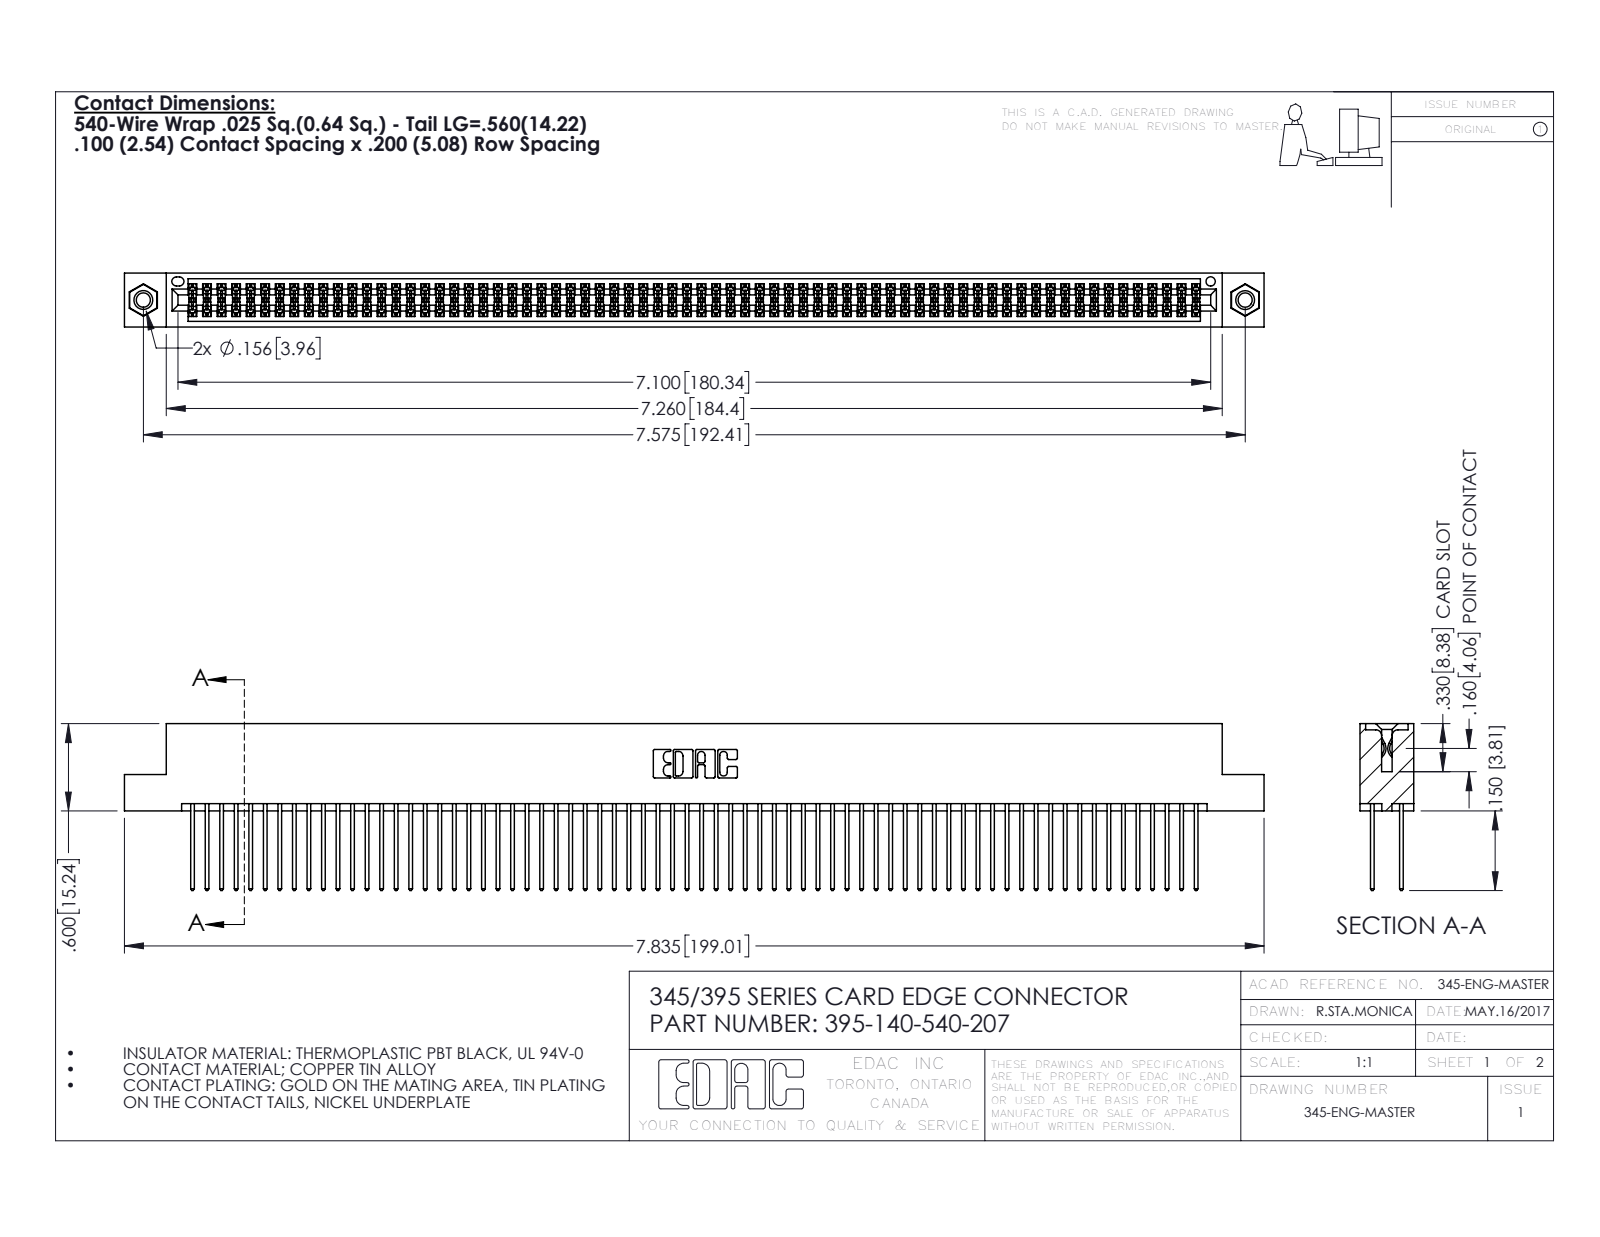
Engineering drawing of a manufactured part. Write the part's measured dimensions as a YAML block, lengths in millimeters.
part_name: "345 Part_Flush Mounting Lugs - 0.156 Dia-TI; 345-250-001_345-250-005-103; 345-292-001_345-293-140; 395-140-540-207"
step_written_by: "SolidWorks 2016 (CONFIG_CONTROL_DESIGN)"
units: millimeters
bodies: {solids: 143, faces: 7186, planar: 4732, cylindrical: 2438, other: 16}
overall_size: [199, 29.1, 9.4]
volume: 20110
surface_area: 32750
round_holes:
  - {diameter: 2.5, count: 2}
  - {diameter: 3.2, count: 2}
  - {diameter: 4, count: 2}
  - {diameter: 1.6, count: 1}
round_bosses_or_shafts:
  - {diameter: 3.9, count: 2}
partial_cylinders:
  - {radius: 0.2, count: 210}
  - {radius: 0.3, count: 140}
  - {radius: 0.3, count: 22}
  - {radius: 0.2, count: 6}
  - {radius: 0.8, count: 6}
  - {radius: 0.7, count: 3}
  - {radius: 0.4, count: 2}
  - {radius: 0.5, count: 2}
face_to_face_distances: [1.8, 7.6, 5.1, 2.5, 6.9, 0.6, 5.7, 9.4, 4.4, 3.8]
hole_center_spacings: [6.9, 186.4, 192.4]
